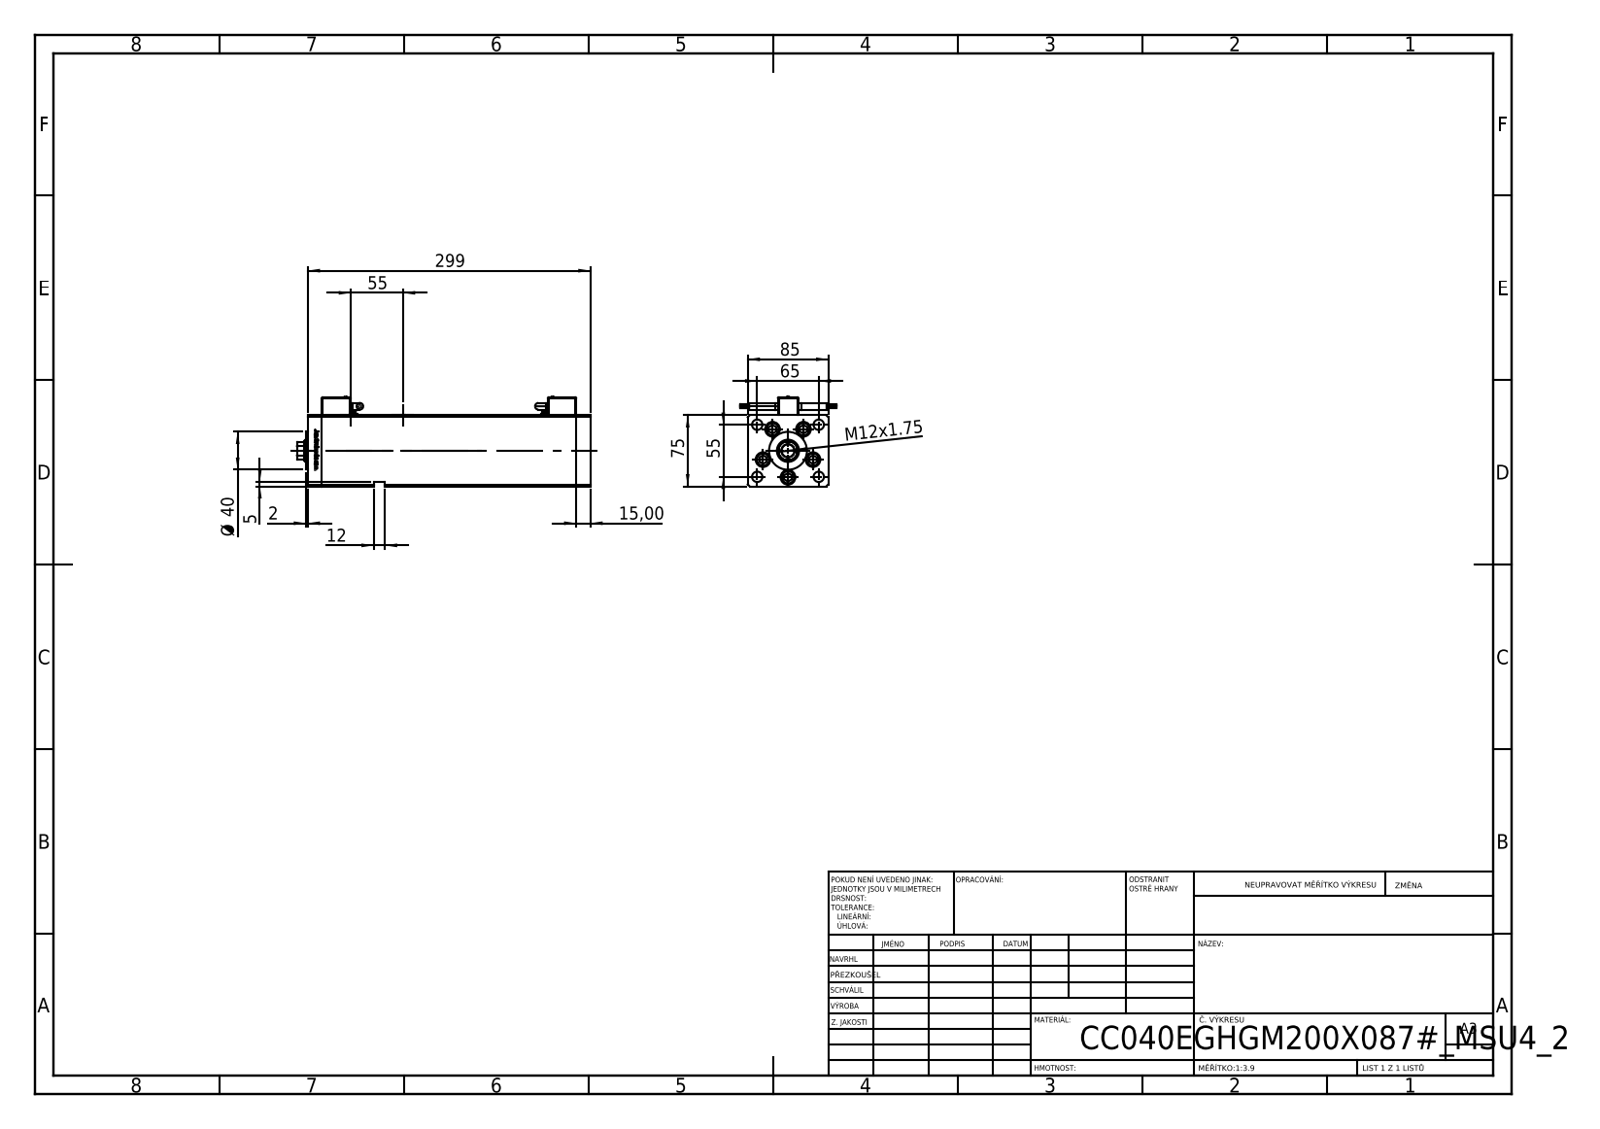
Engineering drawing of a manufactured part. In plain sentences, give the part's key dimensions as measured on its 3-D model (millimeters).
The part is named "V220C_FRONT_E; Magnetic_Switch_MSU4; ALLEN BOLT; V220C BACK_E (+2 more)". Its 3-D file was written by "SolidWorks 2019 (CONFIG_CONTROL_DESIGN)". It is 16 solids with 1416 faces: 551 planar, 255 cylindrical and 610 other. Overall it measures 310 by 101.6 by 95.1 millimeters. Its volume is 1 643 000 cubic millimeters and its surface area 247 578 square millimeters. Round holes: 9 of diameter 11, 5 of diameter 15.5, 4 of diameter 10.5, 4 of diameter 16.5, 2 of diameter 2, 2 of diameter 3.6, 2 of diameter 5, 2 of diameter 7, 2 of diameter 13.16, 1 of diameter 13.5, 1 of diameter 22, 1 of diameter 23.5. Round bosses or shafts: 8 of diameter 0.85, 5 of diameter 14.5, 5 of diameter 8, 4 of diameter 7, 2 of diameter 6, 2 of diameter 3.5, 2 of diameter 2.5, 1 of diameter 40. Partial cylindrical surfaces (rounded edges, fillets, slot ends): 24 of radius 1, 4 of radius 4, 2 of radius 0.93, 1 of radius 10.5. The main face-to-face distances are 85, 75, 15, 268.5, 283.5, 68.5, 10.5, 6.5, 4, 298.5. The hole center spacings are 28, 42.57, 55, 65, 85.15, 8.25, 16.86, 19.17.
